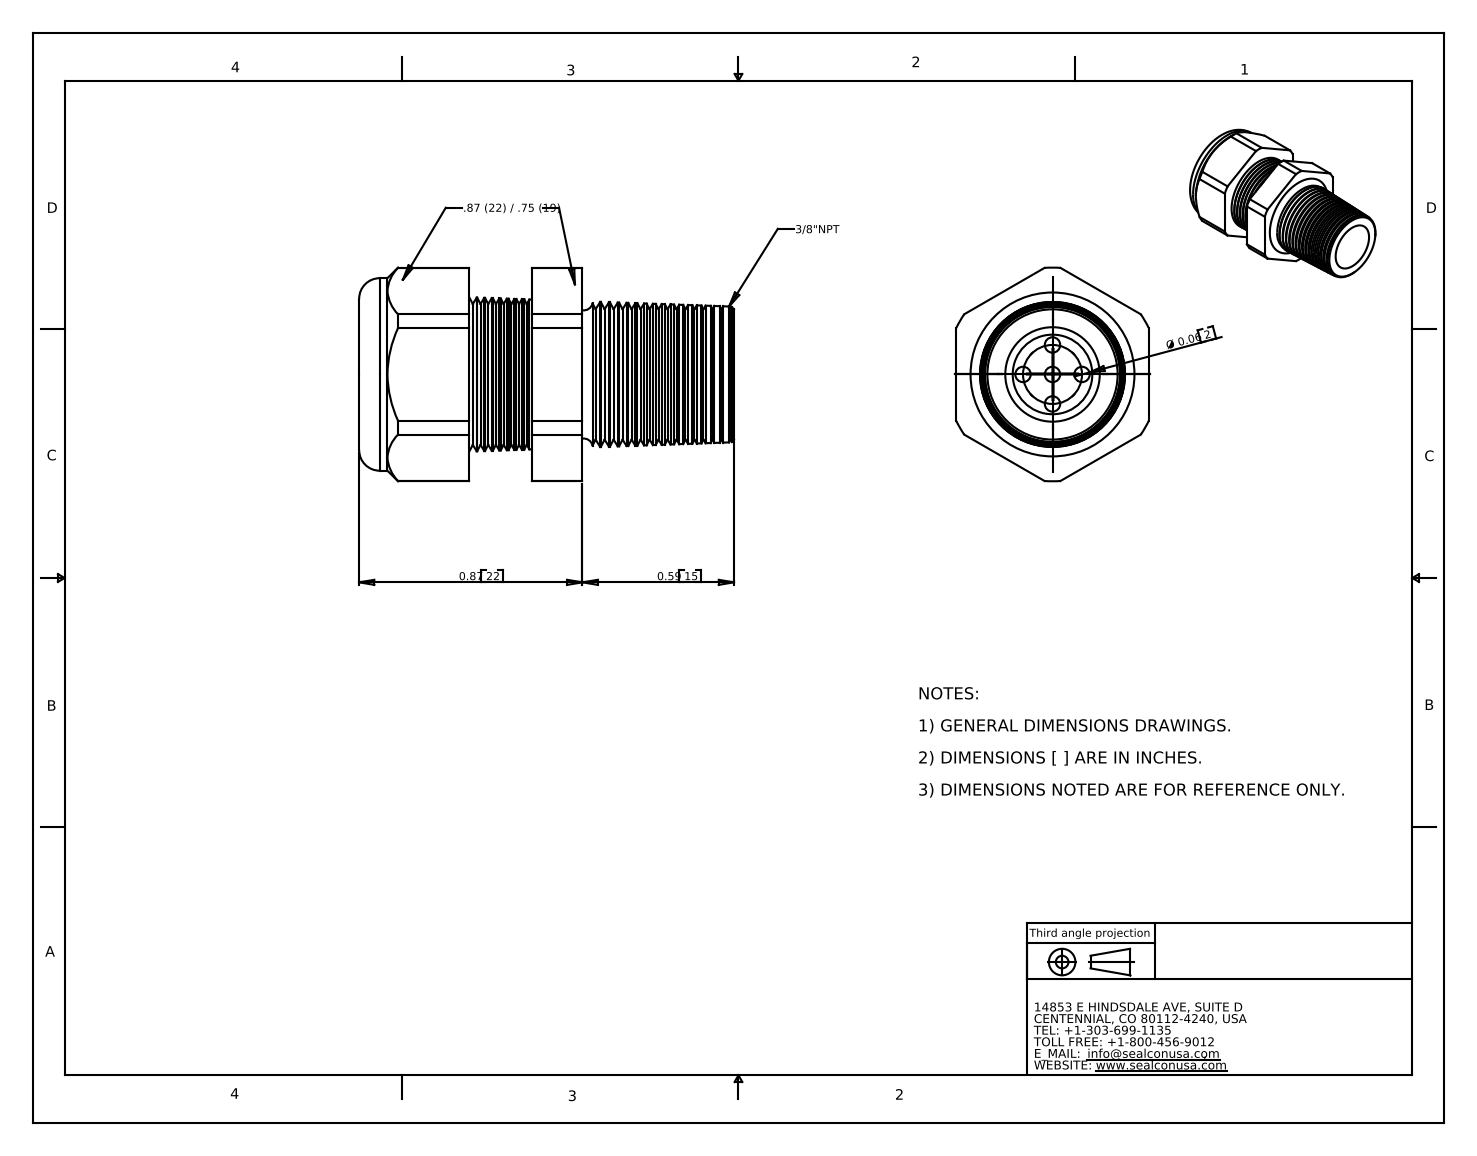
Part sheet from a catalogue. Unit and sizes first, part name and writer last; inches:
Units: inches
Overall size (bounding box): 1.46 × 0.833 × 0.75
Round holes (diameter × count): ⌀0.06 ×5, ⌀0.29 ×1, ⌀0.31 ×1
Round bosses / shafts (diameter × count): ⌀0.75 ×1
Partial cylindrical surfaces — rounded edges, fillets, slot ends (radius × count): R0.416 ×1
Main face-to-face distances: 0.75, 0.673, 0.429, 0.244, 0.75, 0.87, 0.441, 0.197, 1.46, 1.031
Hole centre spacings: 0.115, 0.163, 0.23
Volume: 0.369 in³ · Surface area: 7.051 in²
Bodies: 2 solids, 208 faces (20 planar, 30 cylindrical, 158 other)
Part name (STEP PRODUCT): CD09N3-GY
STEP written by: SolidWorks 2007 (CONFIG_CONTROL_DESIGN)
